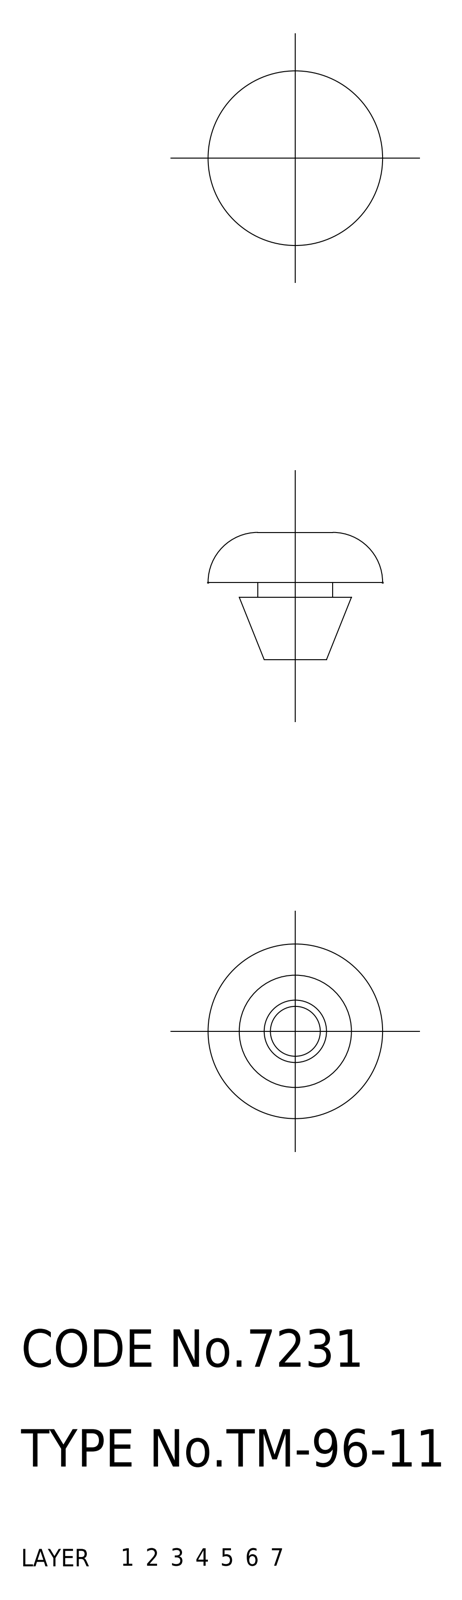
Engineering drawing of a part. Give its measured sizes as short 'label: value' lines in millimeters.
name: cushion
written by: CADfix (AUTOMOTIVE_DESIGN)
unit: mm
bodies: 1 solid, 13 faces (0 planar, 0 cylindrical, 13 other)
size: 14 × 14 × 10.2
volume: 638 mm³; area: 647 mm²
